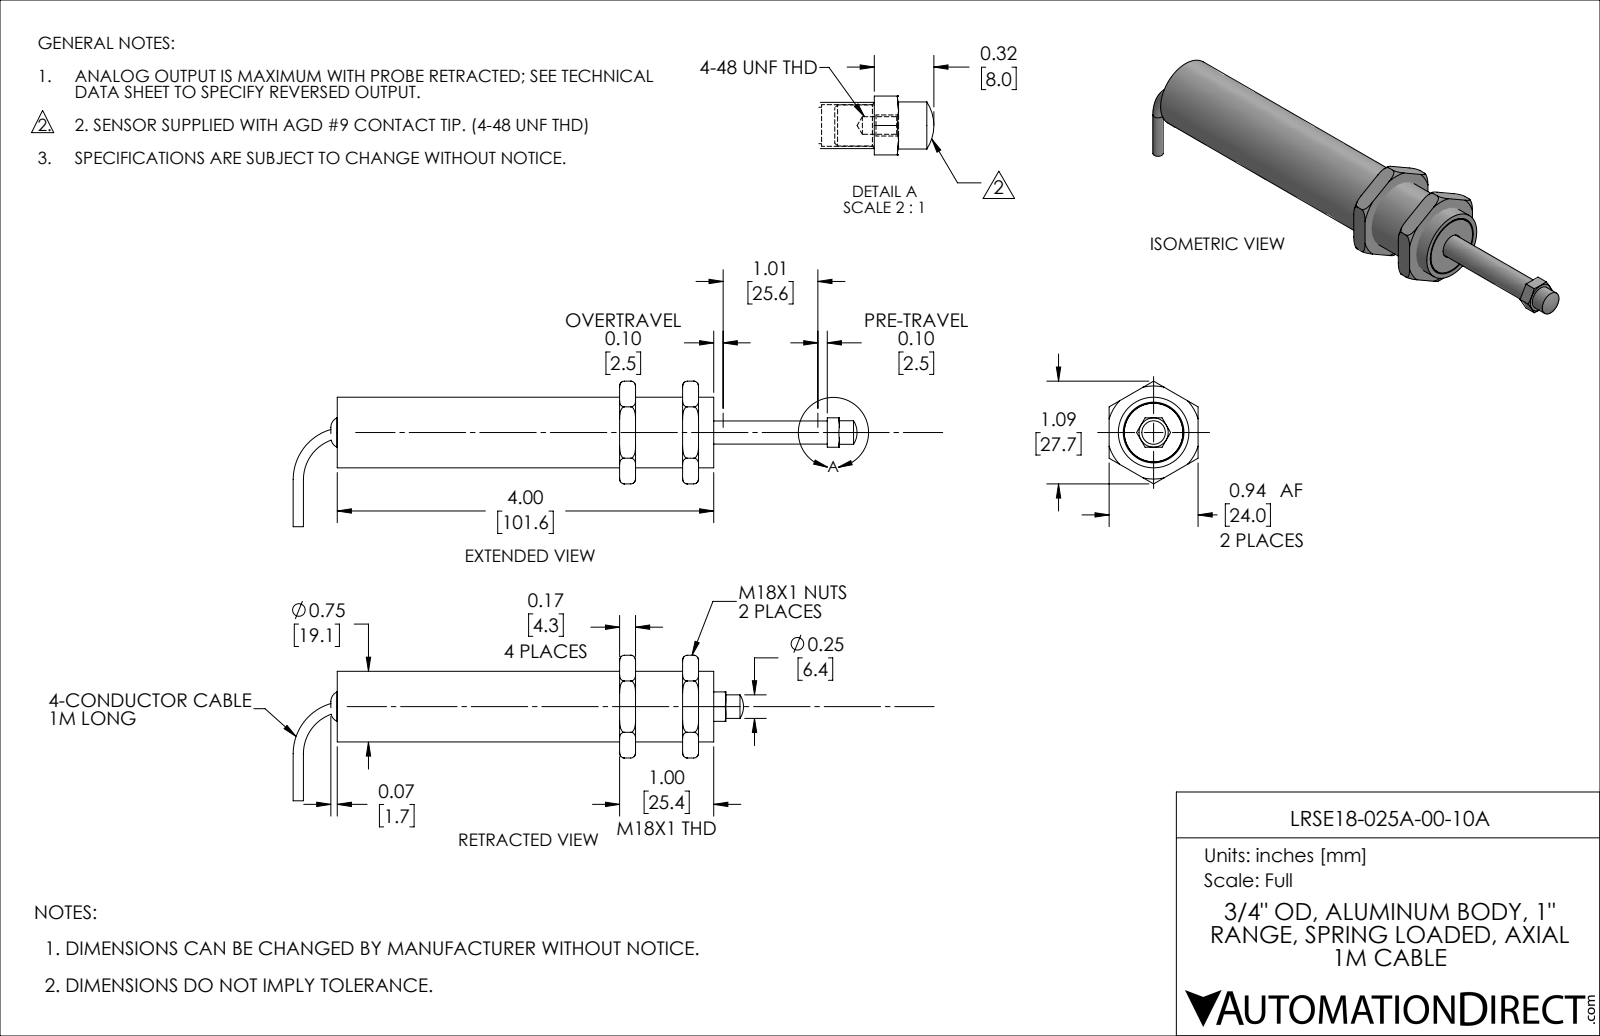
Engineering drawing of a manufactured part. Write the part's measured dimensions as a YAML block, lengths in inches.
part_name: "LRSE18-025A-00-10A"
step_written_by: "SolidWorks 2019 (AUTOMOTIVE_DESIGN)"
units: inches
bodies: {solids: 11, faces: 115, planar: 48, cylindrical: 26, other: 41}
overall_size: [4.785, 1.546, 0.945]
volume: 0.974
surface_area: 29.51
round_holes:
  - {diameter: 0.093, count: 1}
  - {diameter: 0.109, count: 1}
  - {diameter: 0.188, count: 1}
  - {diameter: 0.261, count: 1}
  - {diameter: 0.307, count: 1}
  - {diameter: 0.5, count: 1}
  - {diameter: 0.62, count: 1}
  - {diameter: 0.625, count: 1}
  - {diameter: 0.65, count: 1}
  - {diameter: 0.665, count: 1}
  - {diameter: 0.71, count: 1}
  - {diameter: 0.725, count: 1}
round_bosses_or_shafts:
  - {diameter: 0.75, count: 1}
  - {diameter: 0.7, count: 1}
  - {diameter: 0.685, count: 1}
  - {diameter: 0.624, count: 1}
  - {diameter: 0.25, count: 1}
  - {diameter: 0.218, count: 1}
  - {diameter: 0.112, count: 1}
  - {diameter: 0.109, count: 1}
face_to_face_distances: [0.669, 0.169, 0.945, 3.364, 2.364, 3.033, 1, 0.331, 2.533, 3.203]
